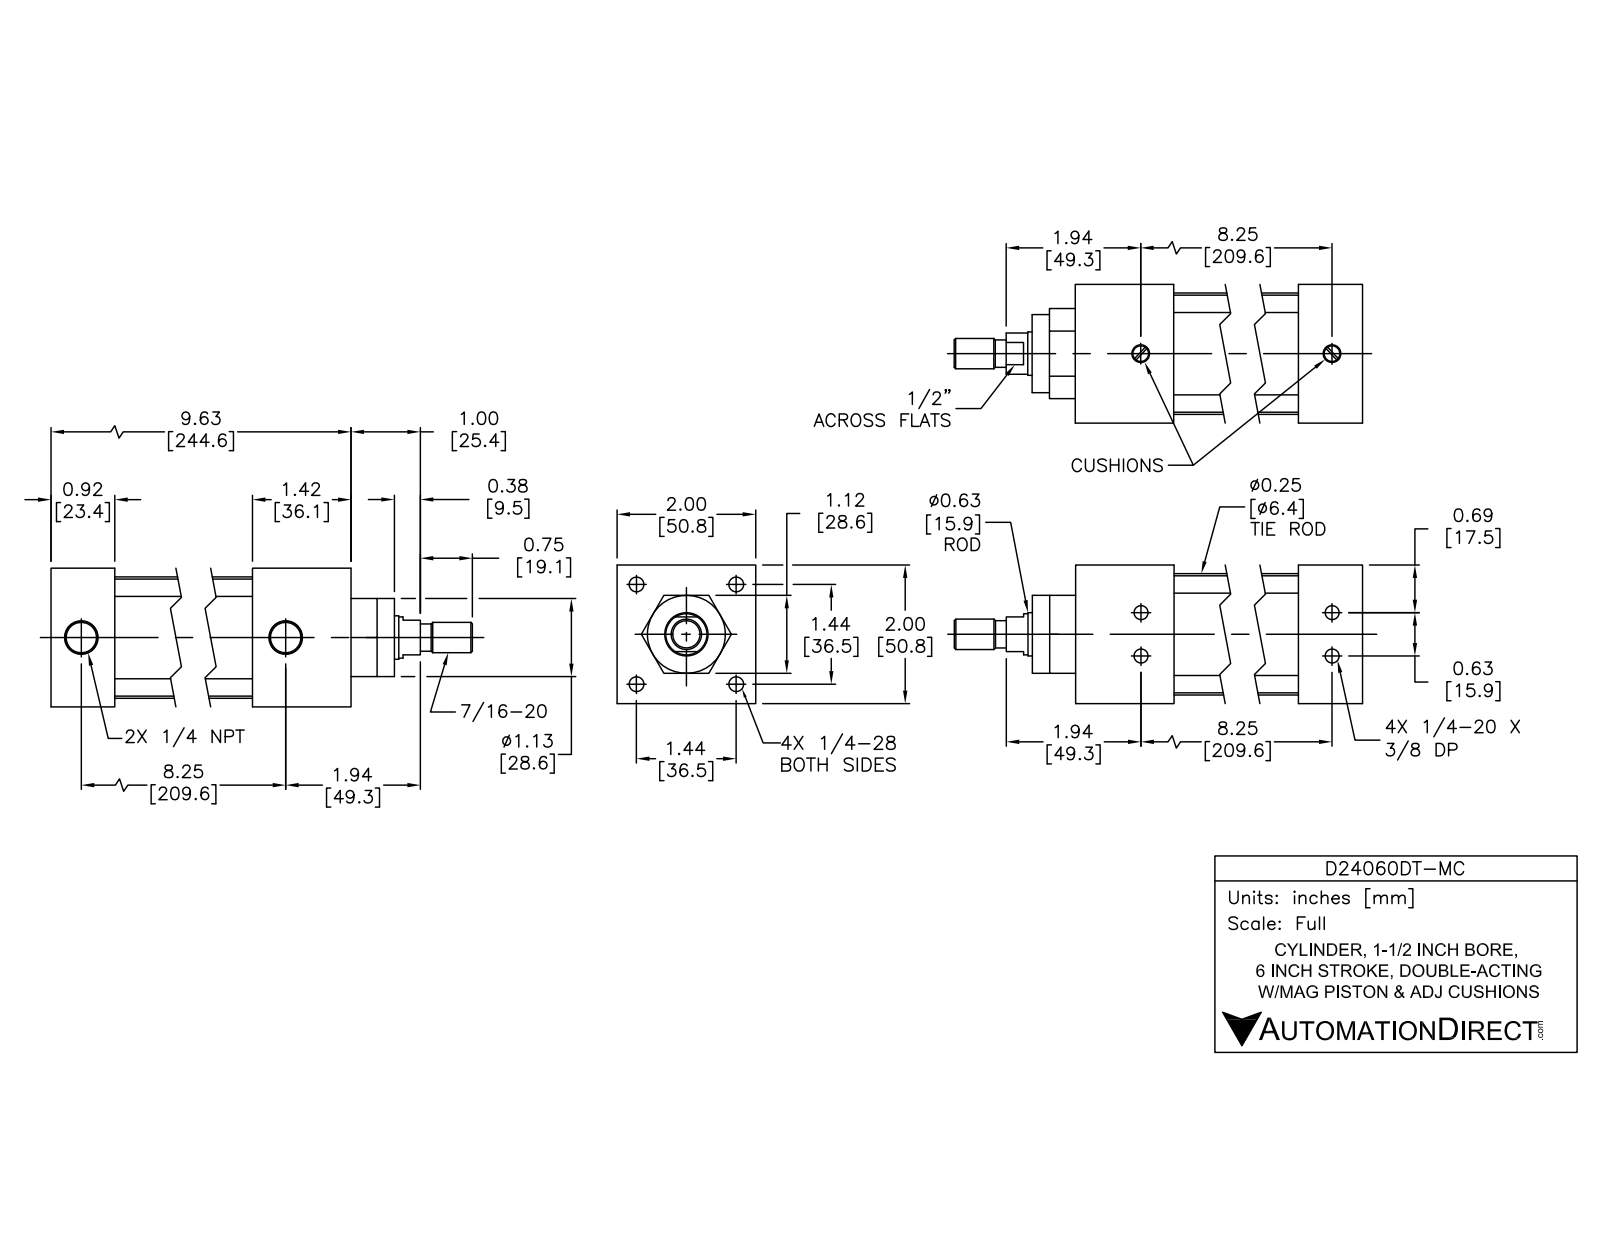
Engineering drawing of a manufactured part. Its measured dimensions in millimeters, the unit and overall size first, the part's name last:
Units: millimetres
Overall size (bounding box): 288.8 × 50.8 × 50.8
Round holes (diameter × count): ⌀5 ×4, ⌀5.4 ×4, ⌀7.1 ×4, ⌀10.3 ×4, ⌀7.5 ×2, ⌀12.1 ×2, ⌀15.9 ×1, ⌀16 ×1, ⌀38.1 ×1
Round bosses / shafts (diameter × count): ⌀9.9 ×4, ⌀6.4 ×4, ⌀5.6 ×4, ⌀44.5 ×1, ⌀38 ×1, ⌀28.5 ×1, ⌀15.8 ×1, ⌀15 ×1
Partial cylindrical surfaces — rounded edges, fillets, slot ends (radius × count): R5.1 ×4
Main face-to-face distances: 50.8, 244.4, 36.1, 208.3, 221, 184.9, 23.4, 28.5, 218.5, 182.4
Hole centre spacings: 8, 25.8, 36.4, 15.9, 51.5, 209.5, 209.6, 209.6
Volume: 315 800 mm³ · Surface area: 117 900 mm²
Bodies: 12 solids, 303 faces (99 planar, 114 cylindrical, 90 other)
Part name (STEP PRODUCT): D24060DT-M BODY; D24060DT-M PISTON; D24060DT-MC
STEP written by: SolidWorks 2015 (AUTOMOTIVE_DESIGN)
